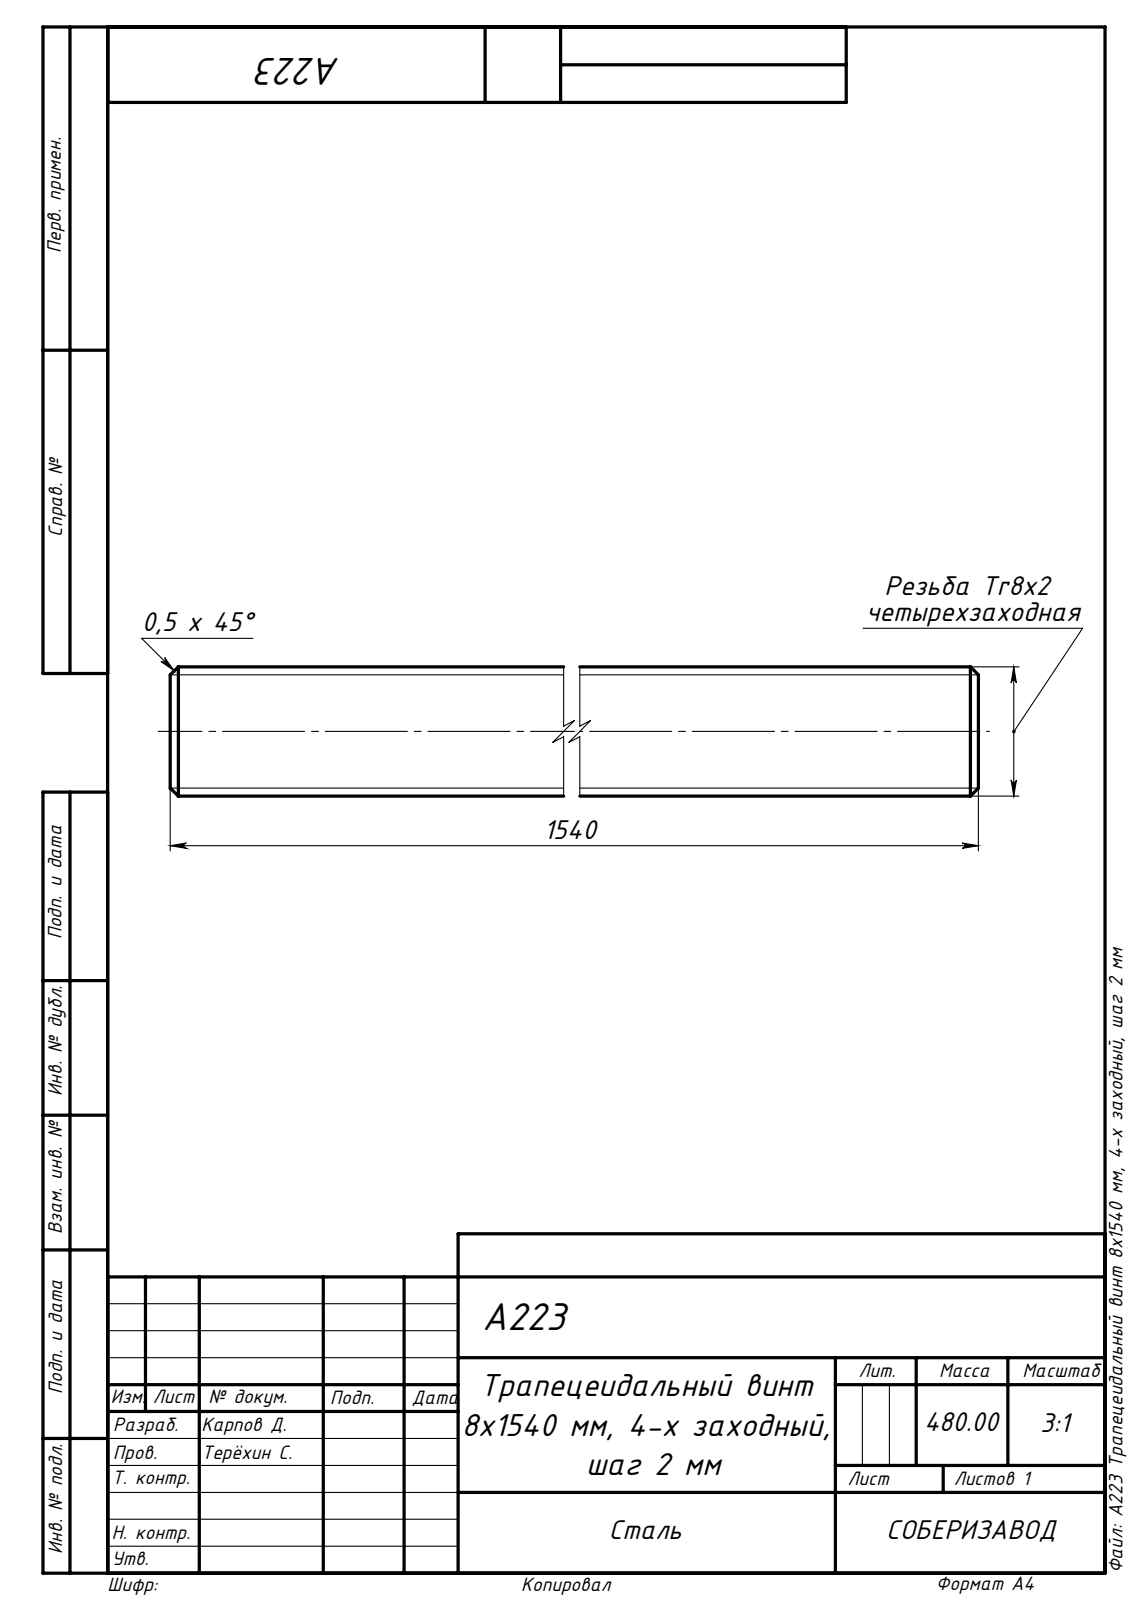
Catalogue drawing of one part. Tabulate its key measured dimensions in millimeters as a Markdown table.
| quantity | value |
| --- | --- |
| part name | A223 Трапецеидальный винт 8х1540 мм, 4-х заходный, шаг 2 мм |
| STEP written by | SolidWorks 2018 (AUTOMOTIVE_DESIGN) |
| units | millimeters |
| bodies | 1 solid, 4 faces (2 planar, 2 cylindrical, 0 other) |
| overall size | 1540 × 8 × 8 |
| volume | 77 409 mm³ |
| surface area | 38 805 mm² |
| round bosses / shafts (diameter × count) | 8 × 1 |
| main face-to-face distances | 1540 |
